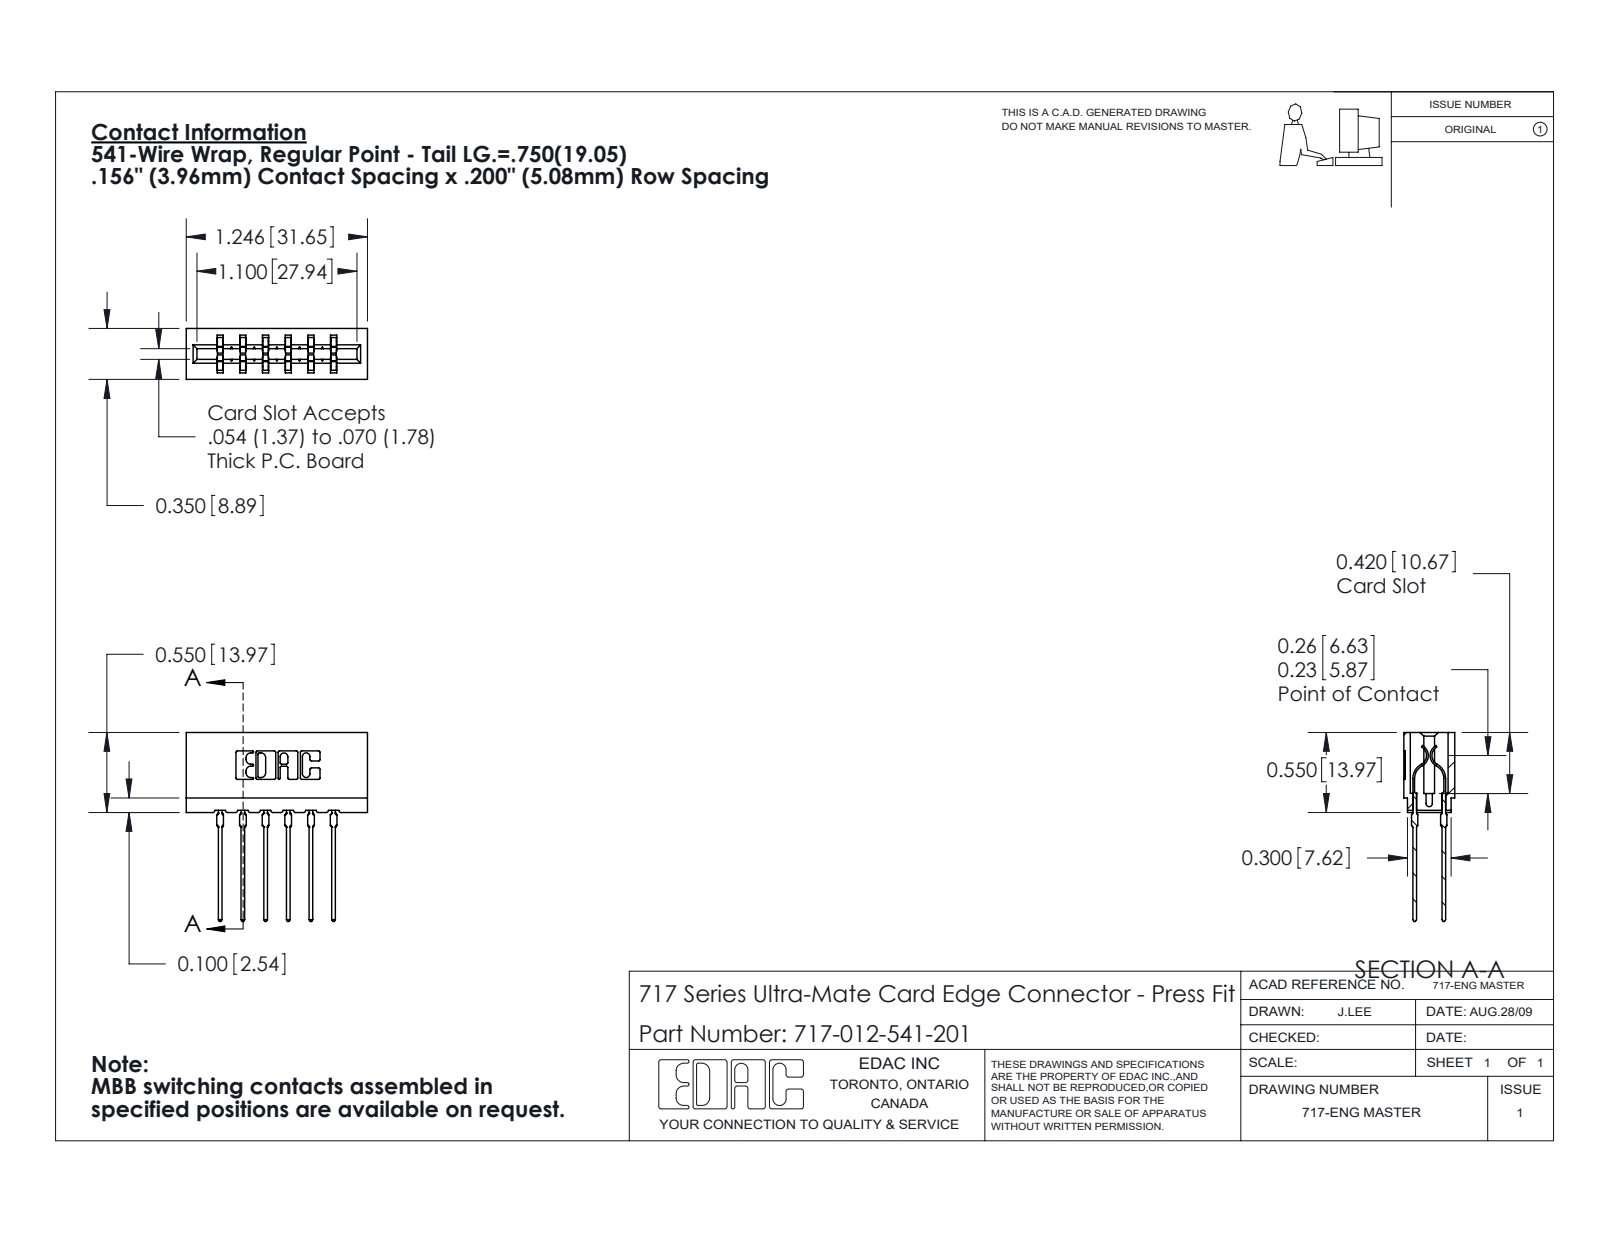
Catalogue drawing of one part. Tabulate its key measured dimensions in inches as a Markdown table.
| quantity | value |
| --- | --- |
| part name | 717-012-541-201; 745-292-001_541; 717 Part_Insulator Option - 06 |
| STEP written by | SolidWorks 2020 (CONFIG_CONTROL_DESIGN) |
| units | inches |
| bodies | 13 solids, 1174 faces (612 planar, 250 cylindrical, 312 other) |
| overall size | 1.299 × 1.246 × 0.35 |
| volume | 0.18 in³ |
| surface area | 6.66 in² |
| partial cylindrical surfaces (radius × count) | 0.021 × 24, 0.01 × 22, 0.015 × 12, 0.005 × 8, 0.011 × 8, 0.007 × 6, 0.031 × 6, 0.026 × 3 |
| main face-to-face distances | 0.156, 0.212, 0.138, 0.35, 0.198, 0.063, 0.287, 0.076, 0.149, 0.312 |
